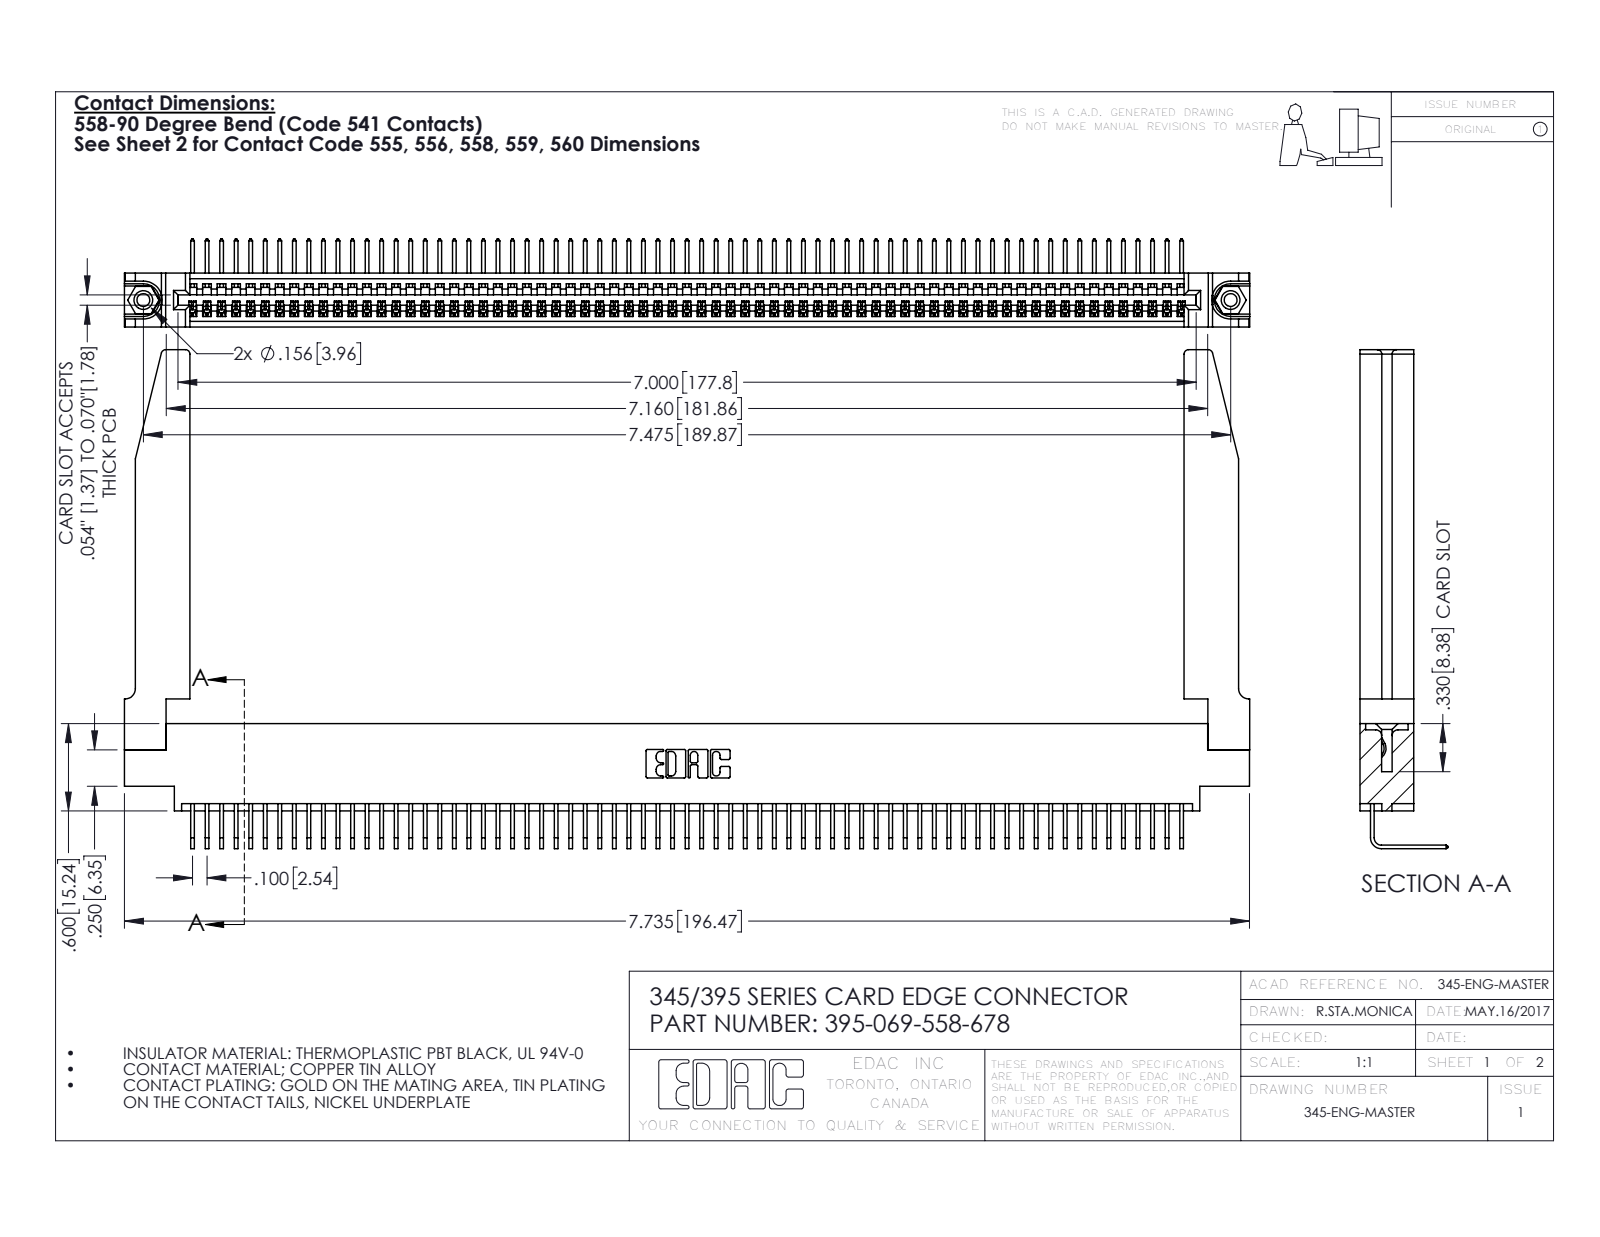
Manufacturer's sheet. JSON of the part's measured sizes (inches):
{"part_name": "345 Part_0.170 Offset - 0.156 Dia-TH; 395-069-558-678; 345-250-001_345-250-001-102; 345-292-001_558 Tail - 2 (+1 more)", "step_written_by": "SolidWorks 2016 (CONFIG_CONTROL_DESIGN)", "units": "inches", "bodies": {"solids": 74, "faces": 4504, "planar": 3124, "cylindrical": 1328, "other": 52}, "overall_size": [7.736, 3.429, 0.605], "volume_in3": 1.634, "surface_area_in2": 52.61, "round_holes": [[0.089, 2], [0.125, 2], [0.156, 2], [0.064, 1]], "round_bosses_or_shafts": [[0.155, 2]], "partial_cylinders_radius": [[0.006, 138], [0.01, 22], [0.03, 8], [0.007, 6], [0.031, 6], [0.026, 3], [0.031, 2], [0.04, 2]], "face_to_face_distances": [0.072, 0.37, 0.298, 0.098, 0.272, 0.025, 0.2, 0.225, 0.175, 0.149], "hole_center_spacings": [0.27, 7.239, 7.475]}
